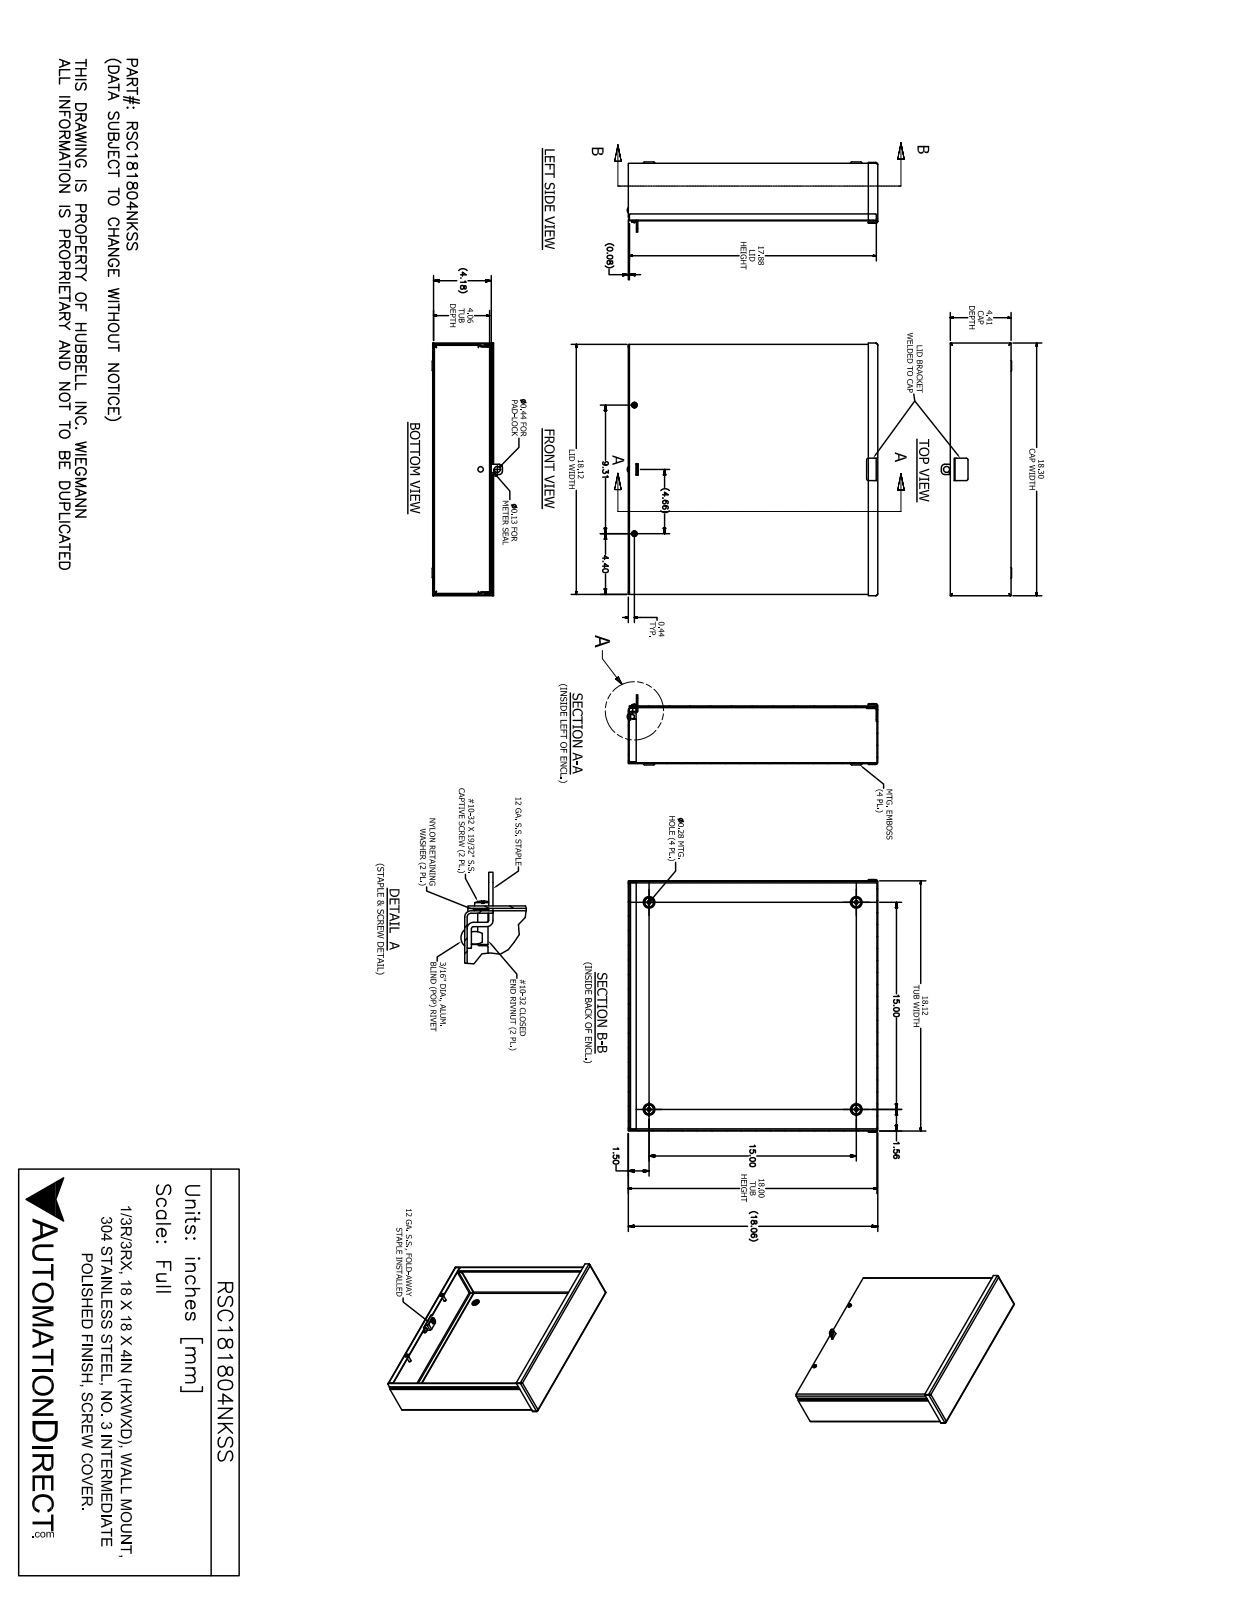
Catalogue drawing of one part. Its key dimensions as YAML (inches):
part_name: "RSC181804NKSS"
step_written_by: "SolidWorks 2017 (AUTOMOTIVE_DESIGN)"
units: inches
bodies: {solids: 13, faces: 383, planar: 199, cylindrical: 99, other: 85}
overall_size: [18.299, 18.149, 5.084]
volume: 59.79
surface_area: 2042
round_holes:
  - {diameter: 0.25, count: 4}
  - {diameter: 0.281, count: 4}
  - {diameter: 0.156, count: 2}
  - {diameter: 0.196, count: 2}
  - {diameter: 0.257, count: 2}
  - {diameter: 0.278, count: 2}
  - {diameter: 0.125, count: 1}
  - {diameter: 0.198, count: 1}
  - {diameter: 0.201, count: 1}
  - {diameter: 0.437, count: 1}
round_bosses_or_shafts:
  - {diameter: 0.453, count: 2}
  - {diameter: 0.406, count: 2}
  - {diameter: 0.248, count: 2}
  - {diameter: 0.167, count: 2}
  - {diameter: 0.187, count: 1}
partial_cylinders:
  - {radius: 0.094, count: 17}
  - {radius: 0.153, count: 17}
  - {radius: 0.031, count: 6}
  - {radius: 0.125, count: 4}
  - {radius: 0.25, count: 4}
  - {radius: 0.062, count: 3}
  - {radius: 0.047, count: 2}
  - {radius: 0.05, count: 2}
face_to_face_distances: [0.059, 4.117, 4.176, 4.058, 18, 18.059, 17.941, 18.118, 0.117, 0.059]
hole_center_spacings: [15, 3.036, 3.047, 9.313, 12.203, 12.206, 16.312, 16.343]
